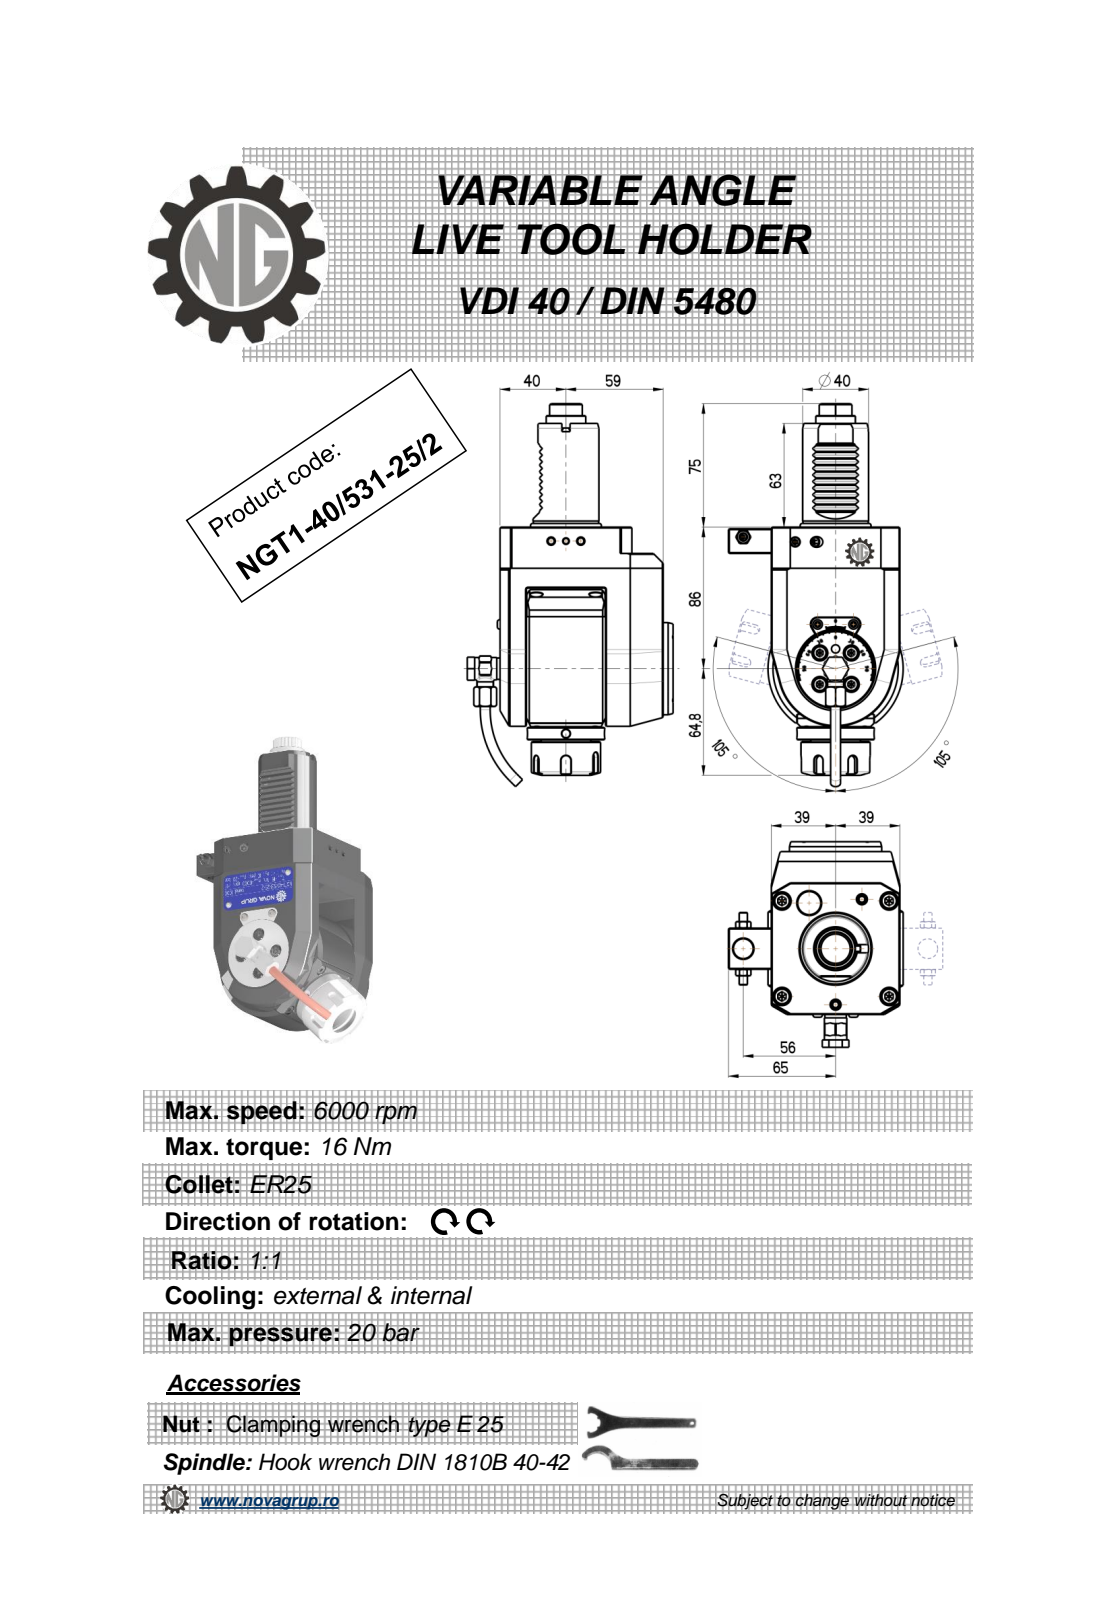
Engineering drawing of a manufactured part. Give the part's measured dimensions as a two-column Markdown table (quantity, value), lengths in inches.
| quantity | value |
| --- | --- |
| part name | NGT1_40_531_25_2 |
| STEP written by | PRO/ENGINEER BY PARAMETRIC TECHNOLOGY CORPORATION, 2010280 (CONFIG_CONTROL_DESIGN) |
| units | inches |
| bodies | 1 solid, 703 faces (254 planar, 241 cylindrical, 208 other) |
| overall size | 9.16 × 4.917 × 4.173 |
| volume | 56.96 in³ |
| surface area | 129.1 in² |
| round holes (diameter × count) | 0.157 × 5, 0.118 × 1, 0.165 × 1, 0.244 × 1, 0.354 × 1, 0.374 × 1, 0.433 × 1, 0.472 × 1, 0.799 × 1 |
| round bosses / shafts (diameter × count) | 0.394 × 2, 0.236 × 2, 0.224 × 2, 2.205 × 1, 1.654 × 1, 1.575 × 1, 1.299 × 1, 0.945 × 1 |
| partial cylindrical surfaces (radius × count) | 0.082 × 48, 0.01 × 12, 0.012 × 10, 0.006 × 6, 0.118 × 5, 0.02 × 4, 0.039 × 2, 0.394 × 2 |
| main face-to-face distances | 0.63, 1.457, 3.898, 3.071, 2.52, 0.236, 4.134, 0.827, 1.614, 0.039 |
| hole center spacings | 0.016, 1.533, 1.929, 1.945, 2.205, 2.93, 2.94, 3.844 |
